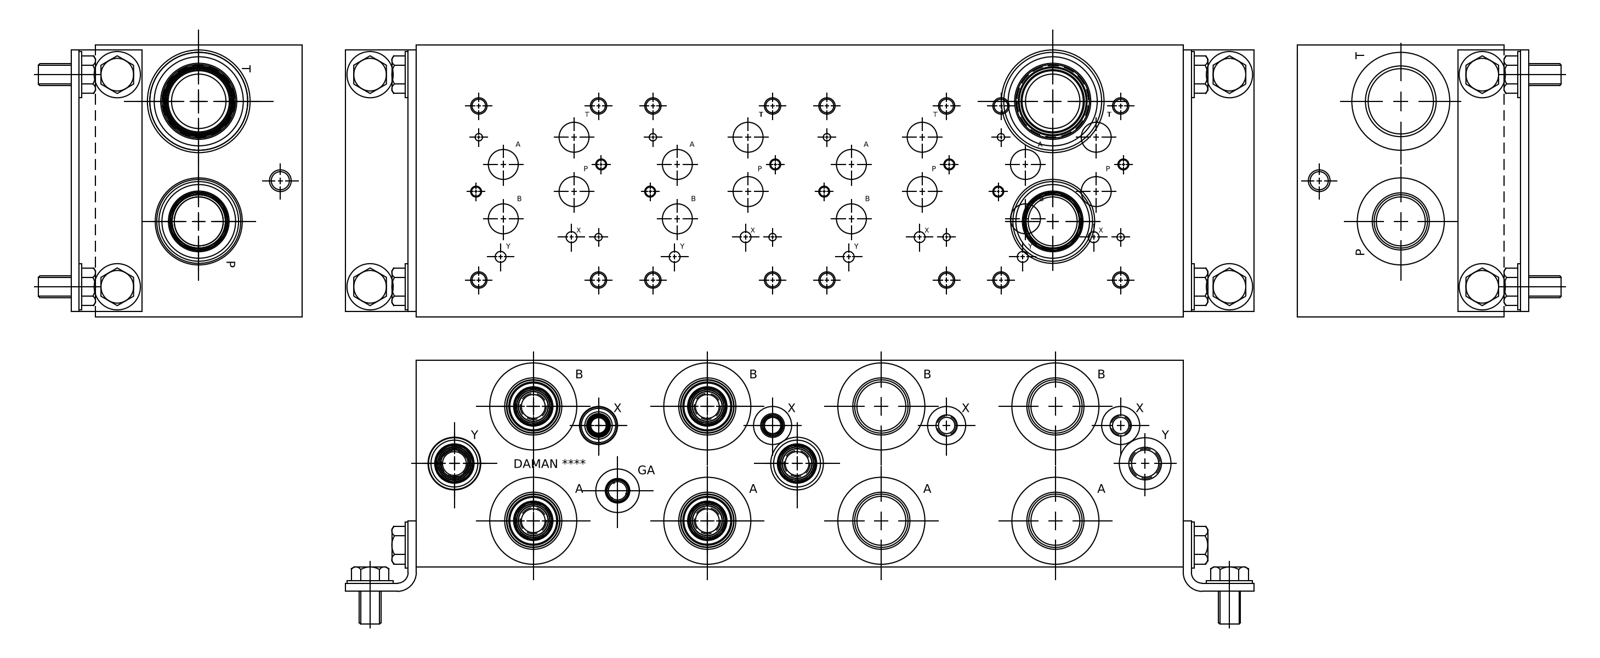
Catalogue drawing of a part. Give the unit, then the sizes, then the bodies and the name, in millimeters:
Units: millimetres
Overall size (bounding box): 447.68 × 158.75 × 120.65
Round holes (diameter × count): ⌀9.53 ×20, ⌀19.05 ×18, ⌀7.92 ×16, ⌀27 ×9, ⌀31.27 ×9, ⌀33.76 ×9, ⌀49.12 ×9, ⌀4.34 ×8, ⌀5.11 ×8, ⌀6.35 ×8, ⌀33.35 ×8, ⌀35.51 ×8
Main face-to-face distances: 120.65, 158.75, 447.68, 0.79, 157.96, 446.89, 446.1, 19.05, 19.84, 138.91
Hole centre spacings: 101.6, 203.2, 123.29, 143.68, 69.85, 121.53, 31.75, 39.69
Volume: 8 063 000 mm³ · Surface area: 371 377 mm²
Bodies: 1 solid, 1058 faces (559 planar, 194 cylindrical, 305 other)
Part name (STEP PRODUCT): Part_AD07HP044S_1_3D
STEP written by: Autodesk Inventor 2020 (AUTOMOTIVE_DESIGN)
